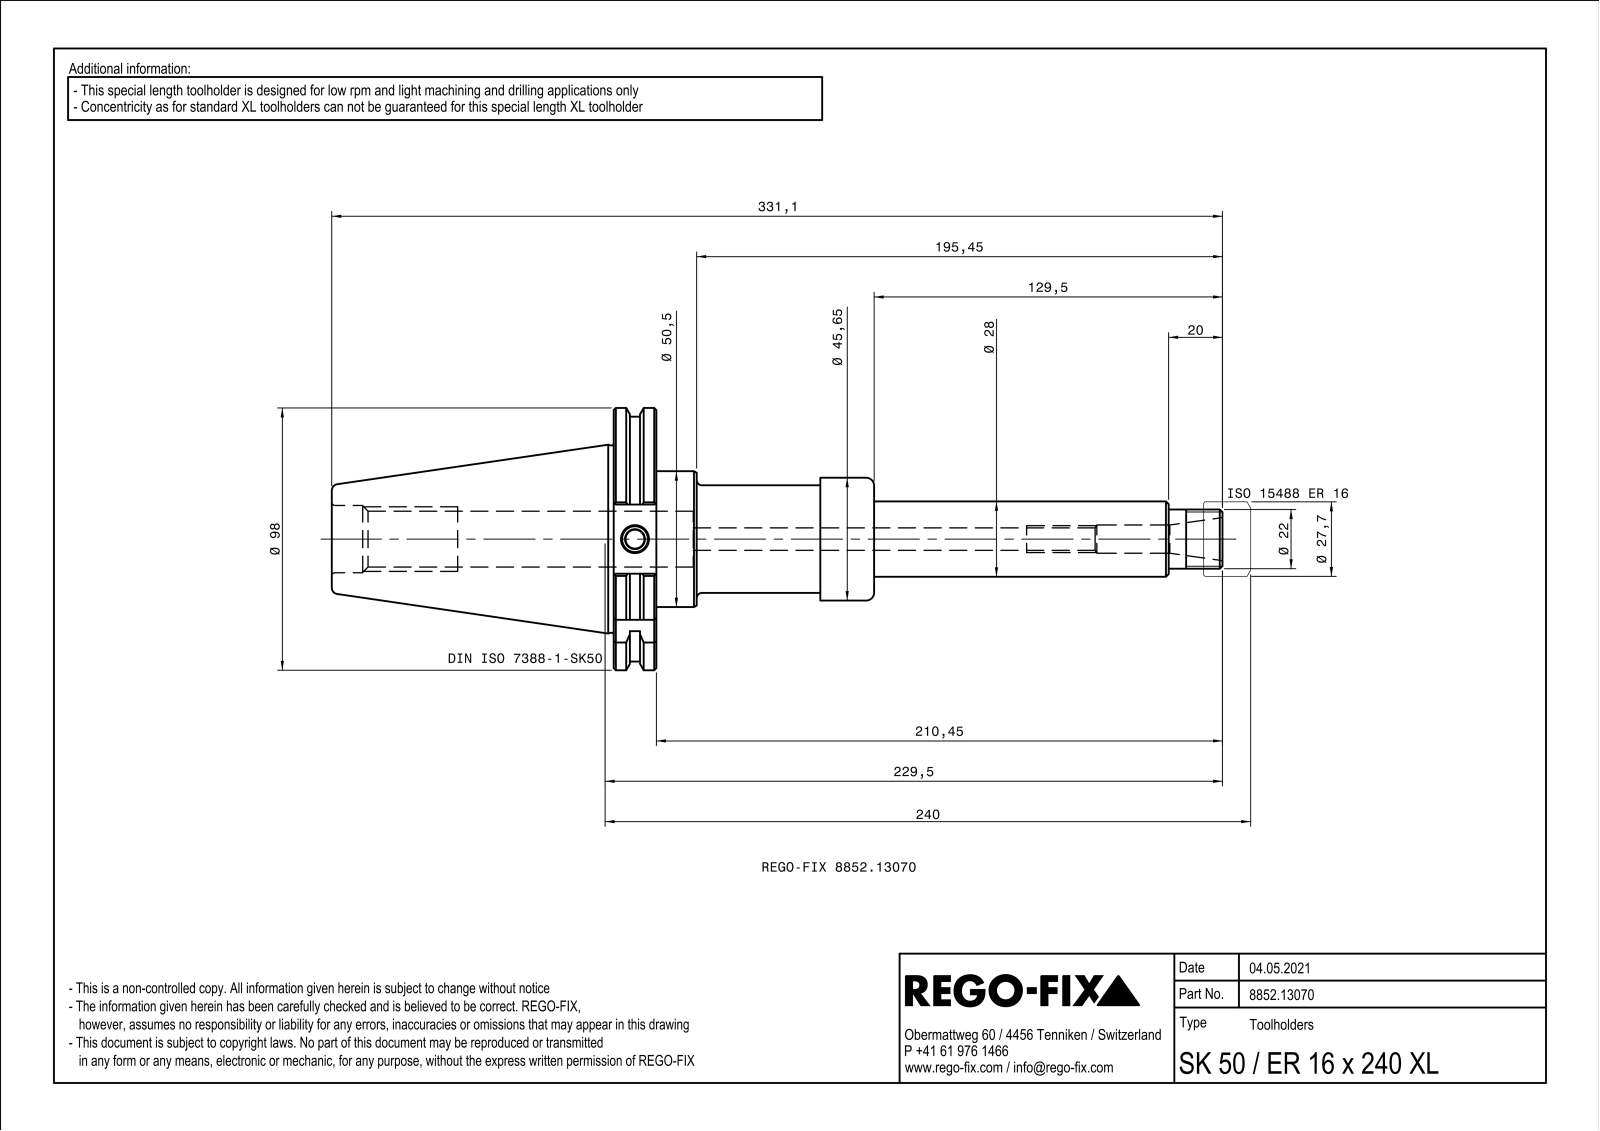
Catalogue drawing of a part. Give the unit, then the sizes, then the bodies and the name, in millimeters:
Units: millimetres
Overall size (bounding box): 331.3 × 97.5 × 93.58
Round holes (diameter × count): ⌀7 ×1, ⌀8.35 ×1, ⌀8.38 ×1, ⌀9.6 ×1, ⌀10 ×1, ⌀10.5 ×1, ⌀20.75 ×1, ⌀25 ×1, ⌀38.38 ×1, ⌀40.05 ×1, ⌀43.3 ×1
Round bosses / shafts (diameter × count): ⌀91 ×1, ⌀50.5 ×1, ⌀45.65 ×1, ⌀40 ×1, ⌀34 ×1, ⌀33.3 ×1, ⌀28.3 ×1, ⌀24.7 ×1
Partial cylindrical surfaces — rounded edges, fillets, slot ends (radius × count): R0.5 ×5, R48.75 ×1
Main face-to-face distances: 15.85, 80.95, 96.8, 6, 14, 201.6, 120.65, 104.8, 20, 65.95
Volume: 490 141 mm³ · Surface area: 79 661 mm²
Bodies: 1 solid, 154 faces (53 planar, 35 cylindrical, 66 other)
Part name (STEP PRODUCT): NOCUT
STEP written by: SIEMENS PLM Software Solid Edge ST10 (AUTOMOTIVE_DESIGN)
